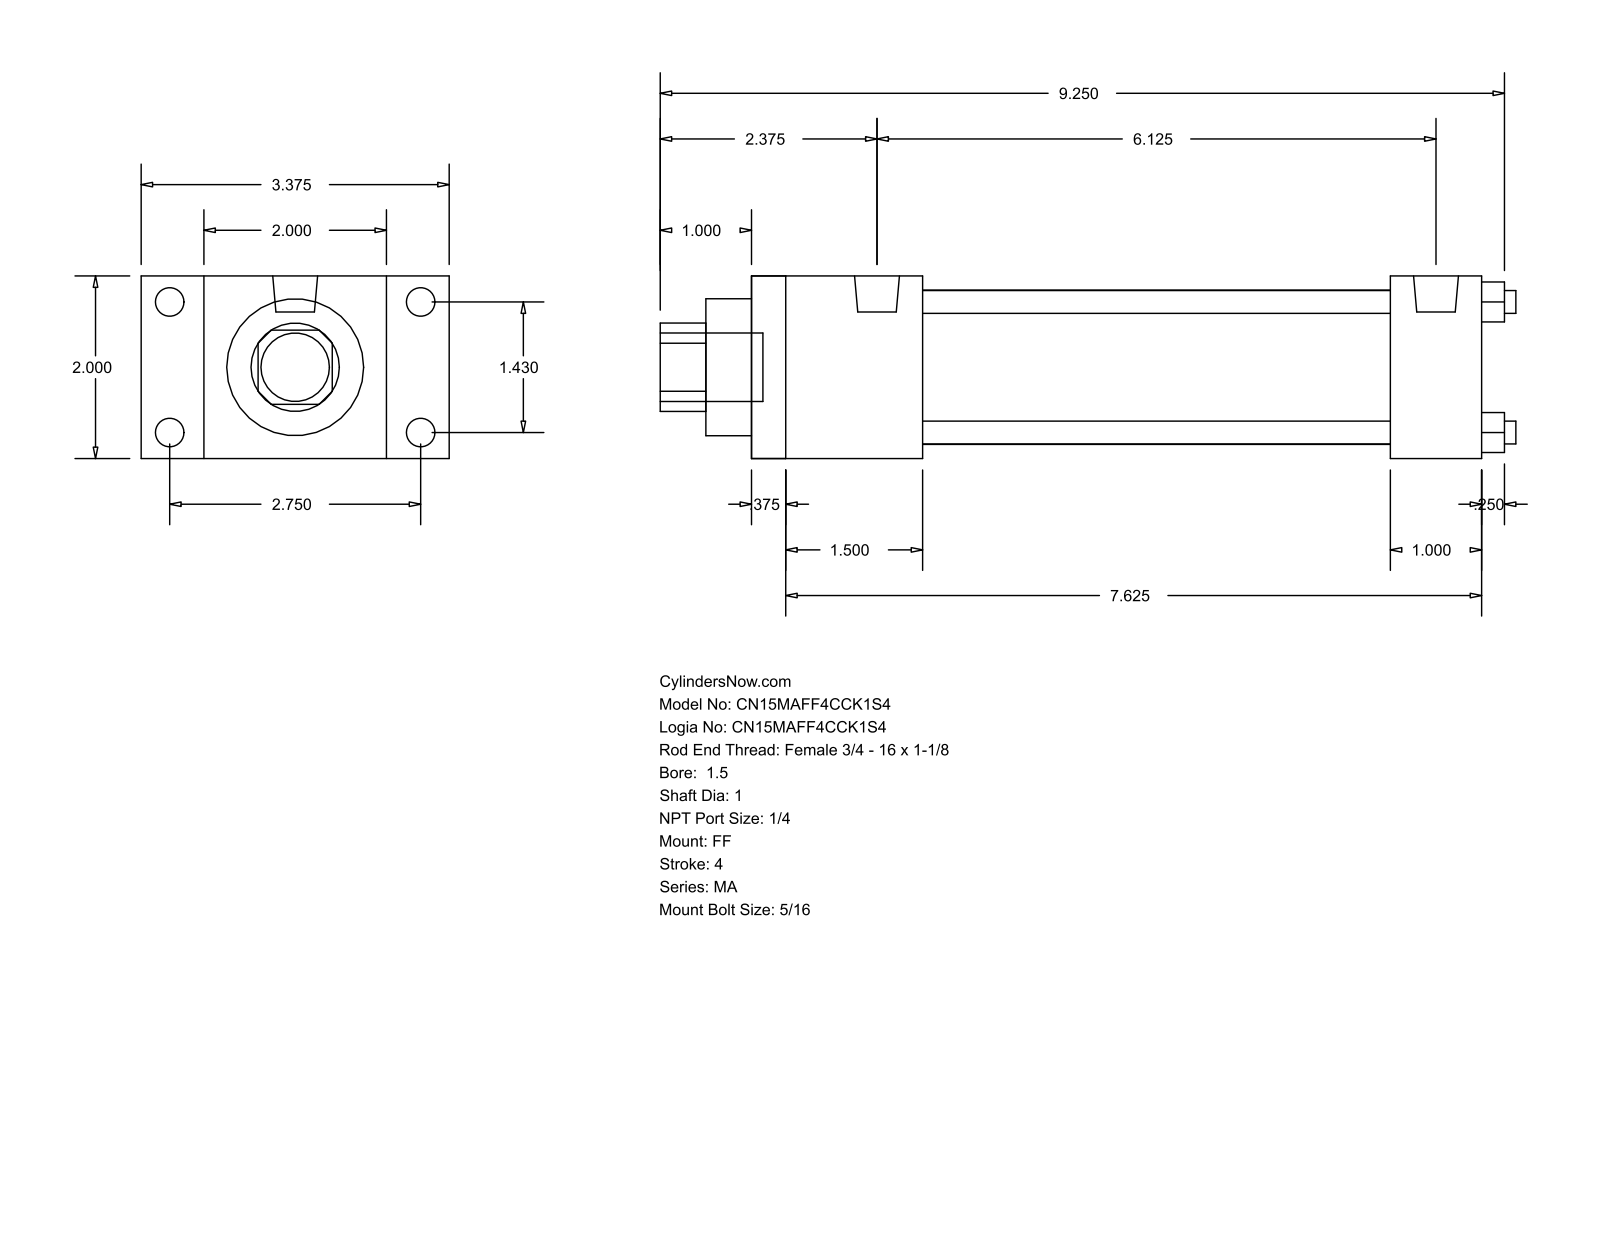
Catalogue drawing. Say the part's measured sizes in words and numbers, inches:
The part is named "MA_FF__0150_1". Its 3-D file was written by "GSSL Pune (CONFIG_CONTROL_DESIGN)". It is 0 solids with 92 faces: 64 planar, 28 cylindrical and 0 other. Overall it measures 9.375 by 3.375 by 2 inches. Round holes: 4 of diameter 0.25, 1 of diameter 1, 1 of diameter 1.5, 1 of diameter 1.69. Round bosses or shafts: 8 of diameter 0.313, 2 of diameter 0.492, 1 of diameter 0.75. Partial cylindrical surfaces (rounded edges, fillets, slot ends): 1 of radius 0.484. The main face-to-face distances are 2, 8, 0.375, 7.625, 1, 1.875, 7, 1.5, 6.625, 5.125. The hole center spacings are 1.011, 1.43, 2.022.
